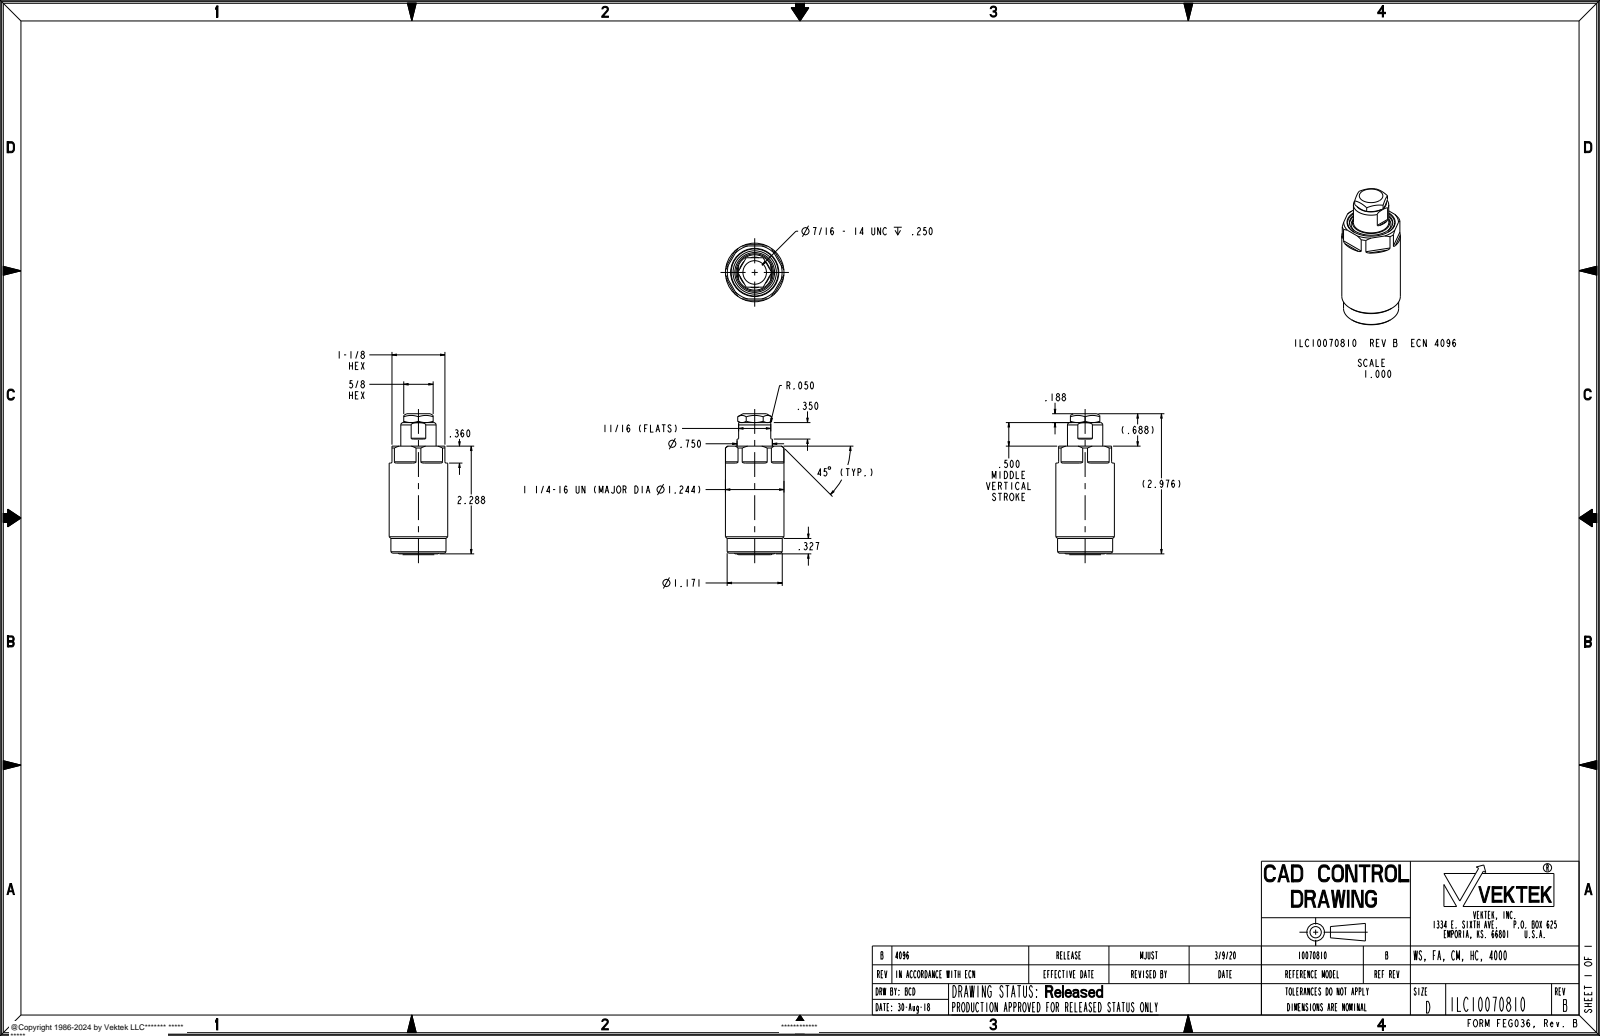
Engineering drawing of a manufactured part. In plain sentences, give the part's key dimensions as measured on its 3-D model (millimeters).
The part is named "ILC10070810". Its 3-D file was written by "PRO/ENGINEER BY PARAMETRIC TECHNOLOGY CORPORATION, 2017170 (AUTOMOTIVE_DESIGN)". It is 1 solid with 90 faces: 34 planar, 26 cylindrical and 30 other. Overall it measures 76 by 31.6 by 31.6 millimeters. Its volume is 47 470 cubic millimeters and its surface area 9 090 square millimeters. Round holes: 1 of diameter 4.8, 1 of diameter 9.3, 1 of diameter 18.9, 1 of diameter 23.4. Round bosses or shafts: 1 of diameter 31.6, 1 of diameter 29.7, 1 of diameter 25.4, 1 of diameter 19.1, 1 of diameter 11.1. Partial cylindrical surfaces (rounded edges, fillets, slot ends): 6 of radius 0.7, 2 of radius 0.5. The main face-to-face distances are 6.4, 28.6, 0.9, 22.2, 56.8, 57.7, 75.2, 74.3, 17.5, 57.5.
